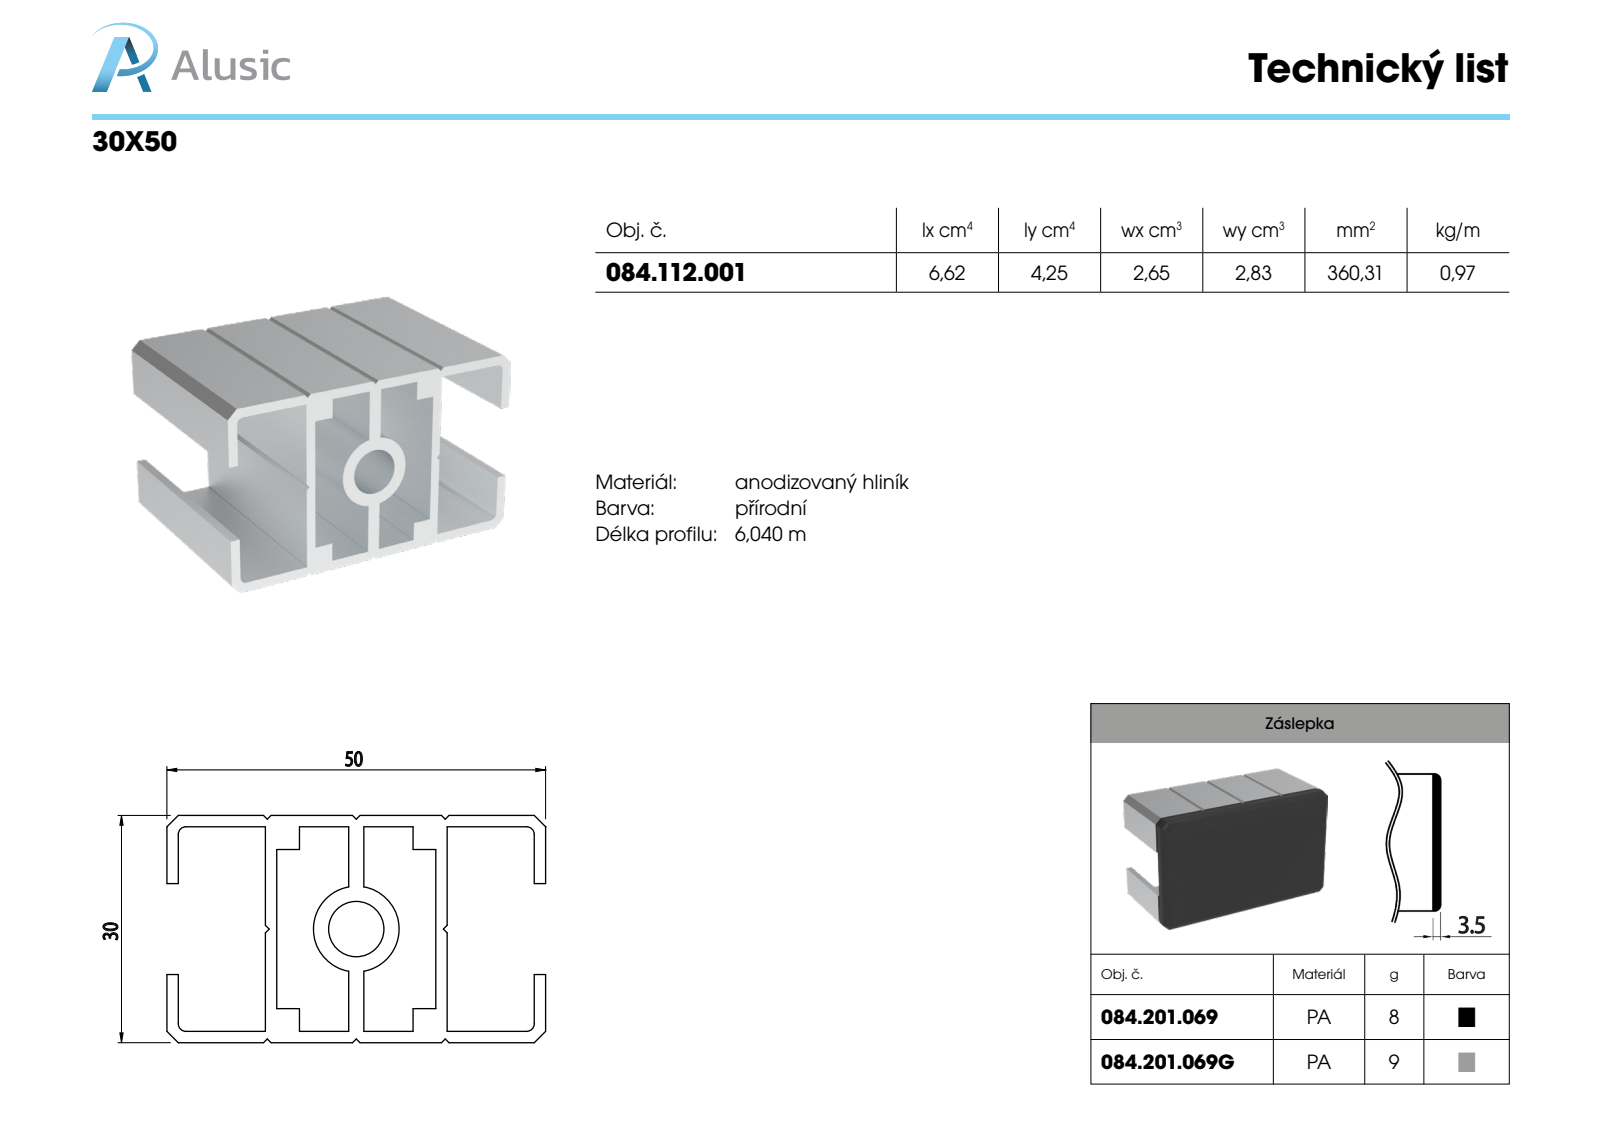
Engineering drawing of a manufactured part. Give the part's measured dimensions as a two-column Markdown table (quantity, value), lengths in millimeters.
| quantity | value |
| --- | --- |
| part name | 084.201.069 |
| STEP written by | SolidWorks 2012 (CONFIG_CONTROL_DESIGN) |
| units | millimeters |
| bodies | 1 solid, 79 faces (46 planar, 25 cylindrical, 8 other) |
| overall size | 50 × 30 × 10.5 |
| volume | 5 405 mm³ |
| surface area | 3 713 mm² |
| round bosses / shafts (diameter × count) | 3.8 × 4 |
| partial cylindrical surfaces (radius × count) | 2 × 8, 2.7 × 1, 2.93 × 1, 3.56 × 1, 3.61 × 1, 6.73 × 1 |
| main face-to-face distances | 3.5, 30, 50, 3.7, 10.5, 7, 6.8, 54.44, 7.62, 42.38 |
